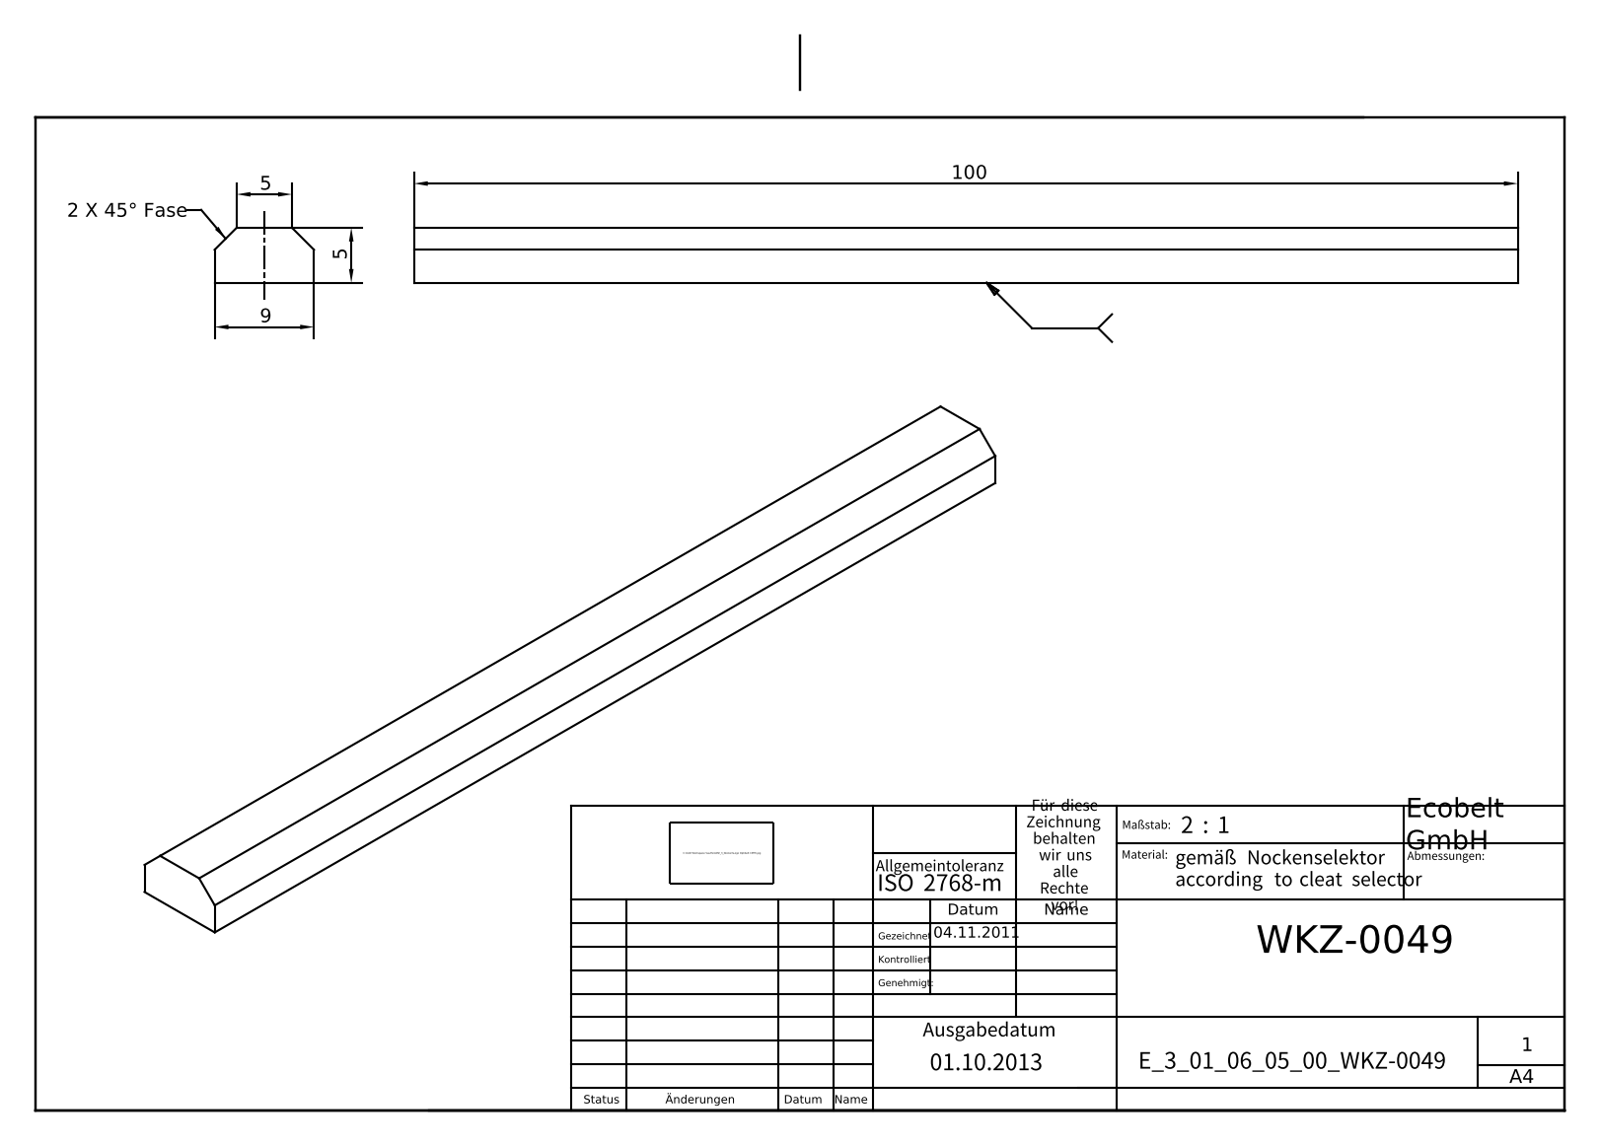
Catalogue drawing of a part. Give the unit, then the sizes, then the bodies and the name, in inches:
Units: inches
Overall size (bounding box): 3.937 × 0.354 × 0.197
Main face-to-face distances: 0.197, 0.354, 3.937
Volume: 0.25 in³ · Surface area: 4.104 in²
Bodies: 1 solid, 8 faces (8 planar, 0 cylindrical, 0 other)
Part name (STEP PRODUCT): E_3_01_06_05_00_WKZ-0049
STEP written by: Autodesk Inventor 2025 (AUTOMOTIVE_DESIGN)
